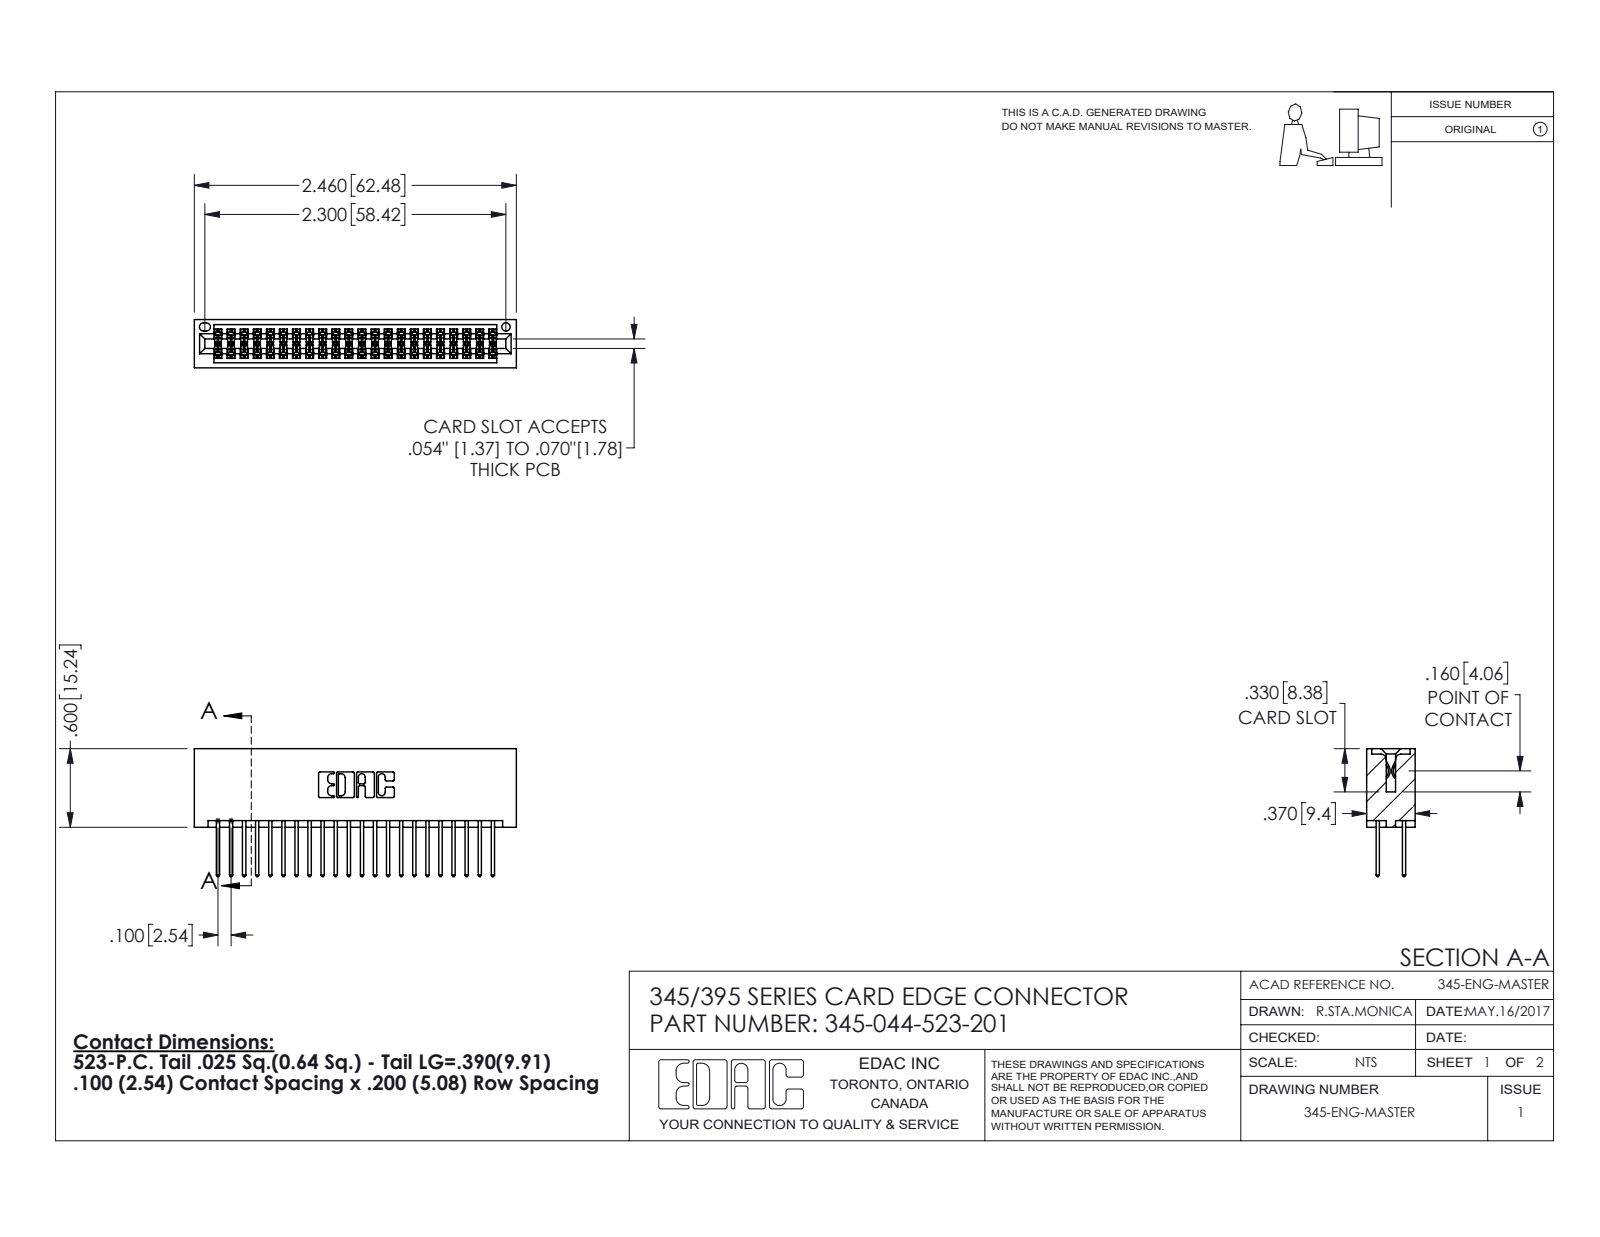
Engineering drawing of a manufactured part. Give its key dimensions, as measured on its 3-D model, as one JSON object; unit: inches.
{"part_name": "345 Part_No Mounting Lugs; 345-044-523-201; 345-292-001_345-293-123", "step_written_by": "SolidWorks 2016 (CONFIG_CONTROL_DESIGN)", "units": "inches", "bodies": {"solids": 45, "faces": 2318, "planar": 1528, "cylindrical": 790, "other": 0}, "overall_size": [2.46, 0.977, 0.37], "volume_in3": 0.402, "surface_area_in2": 15.6, "round_holes": [[0.064, 1]], "partial_cylinders_radius": [[0.006, 66], [0.01, 44], [0.01, 22], [0.007, 6], [0.031, 6], [0.026, 3], [0.014, 2], [0.019, 2]], "face_to_face_distances": [0.298, 0.072, 0.2, 0.098, 0.272, 0.025, 0.37, 0.225, 0.175, 0.1]}
